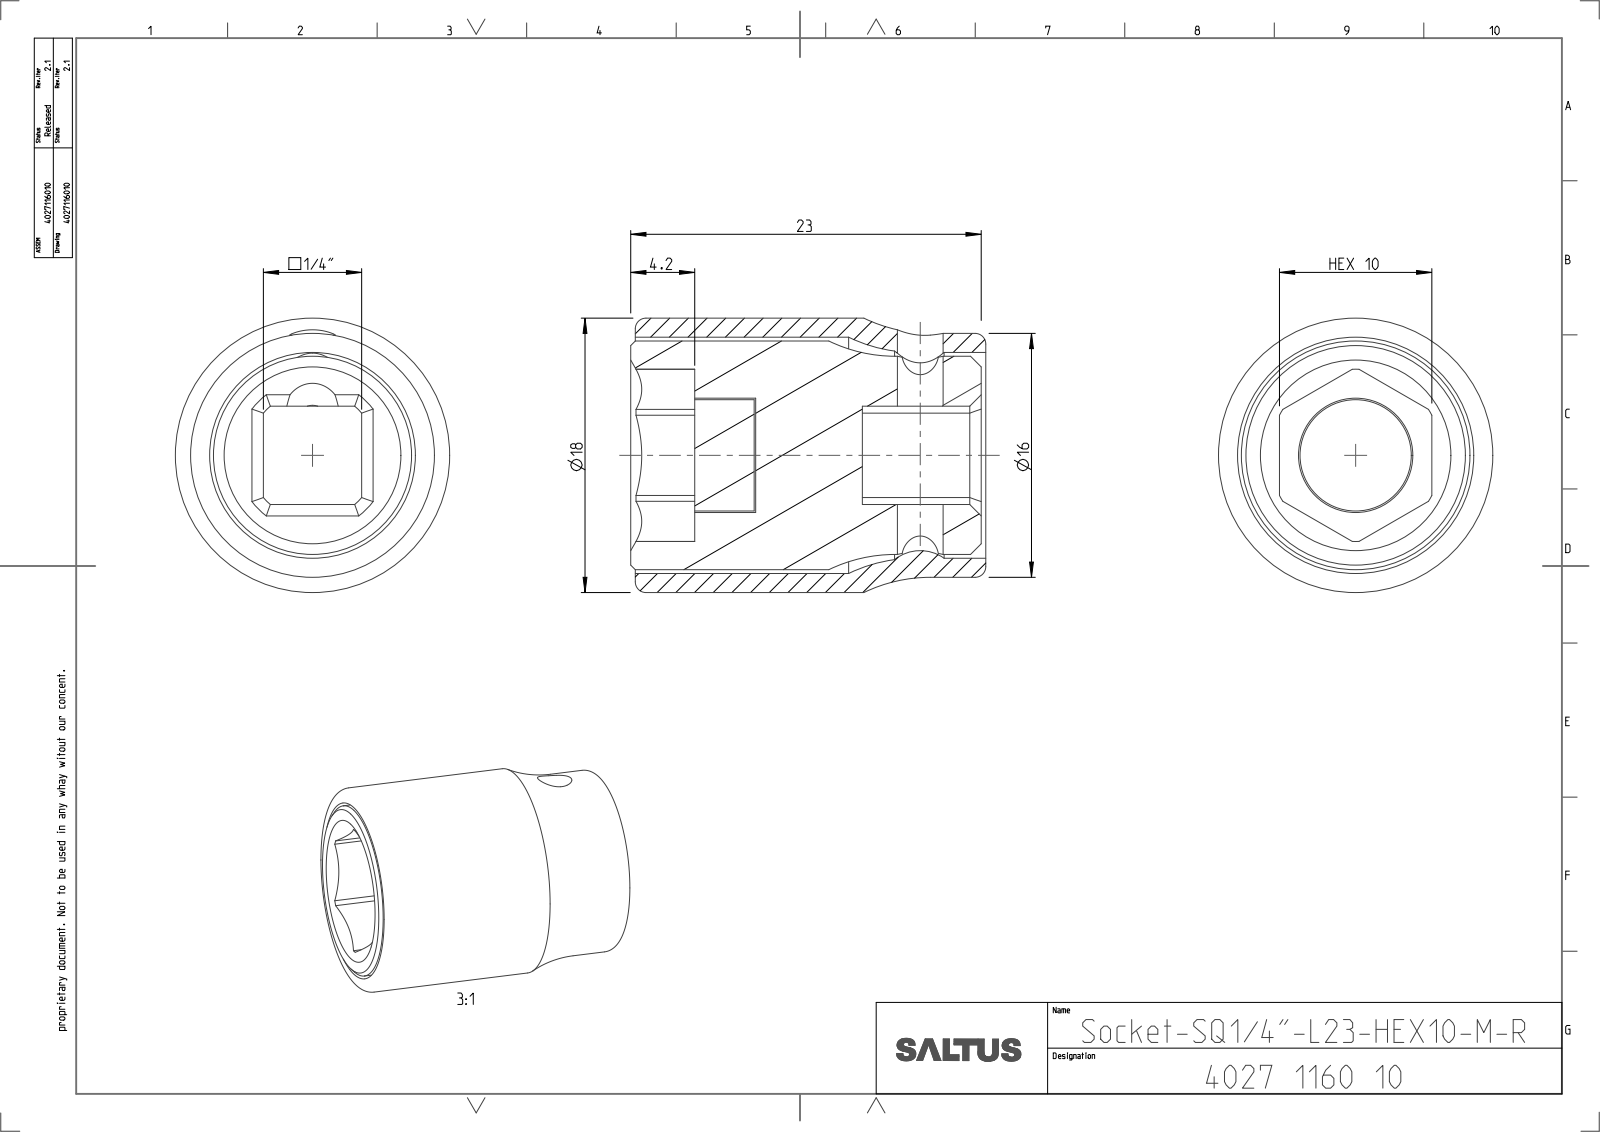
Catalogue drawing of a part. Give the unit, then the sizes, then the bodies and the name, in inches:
Units: inches
Overall size (bounding box): 0.917 × 0.709 × 0.709
Round holes (diameter × count): ⌀0.118 ×1, ⌀0.295 ×1, ⌀0.531 ×1, ⌀0.61 ×1
Round bosses / shafts (diameter × count): ⌀0.709 ×1, ⌀0.63 ×1, ⌀0.591 ×1, ⌀0.512 ×1, ⌀0.287 ×1
Partial cylindrical surfaces — rounded edges, fillets, slot ends (radius × count): R0.079 ×1, R0.167 ×1, R0.222 ×1
Main face-to-face distances: 0.587, 0.154, 0.307, 0.254, 0.319, 0.598, 0.906, 0.394, 0.157, 0.583
Volume: 0.267 in³ · Surface area: 6.801 in²
Bodies: 3 solids, 83 faces (24 planar, 35 cylindrical, 24 other)
Part name (STEP PRODUCT): 4027110510; 4027299222; 4027116010_ASM
STEP written by: CREO PARAMETRIC BY PTC INC, 2022414 (CONFIG_CONTROL_DESIGN)
